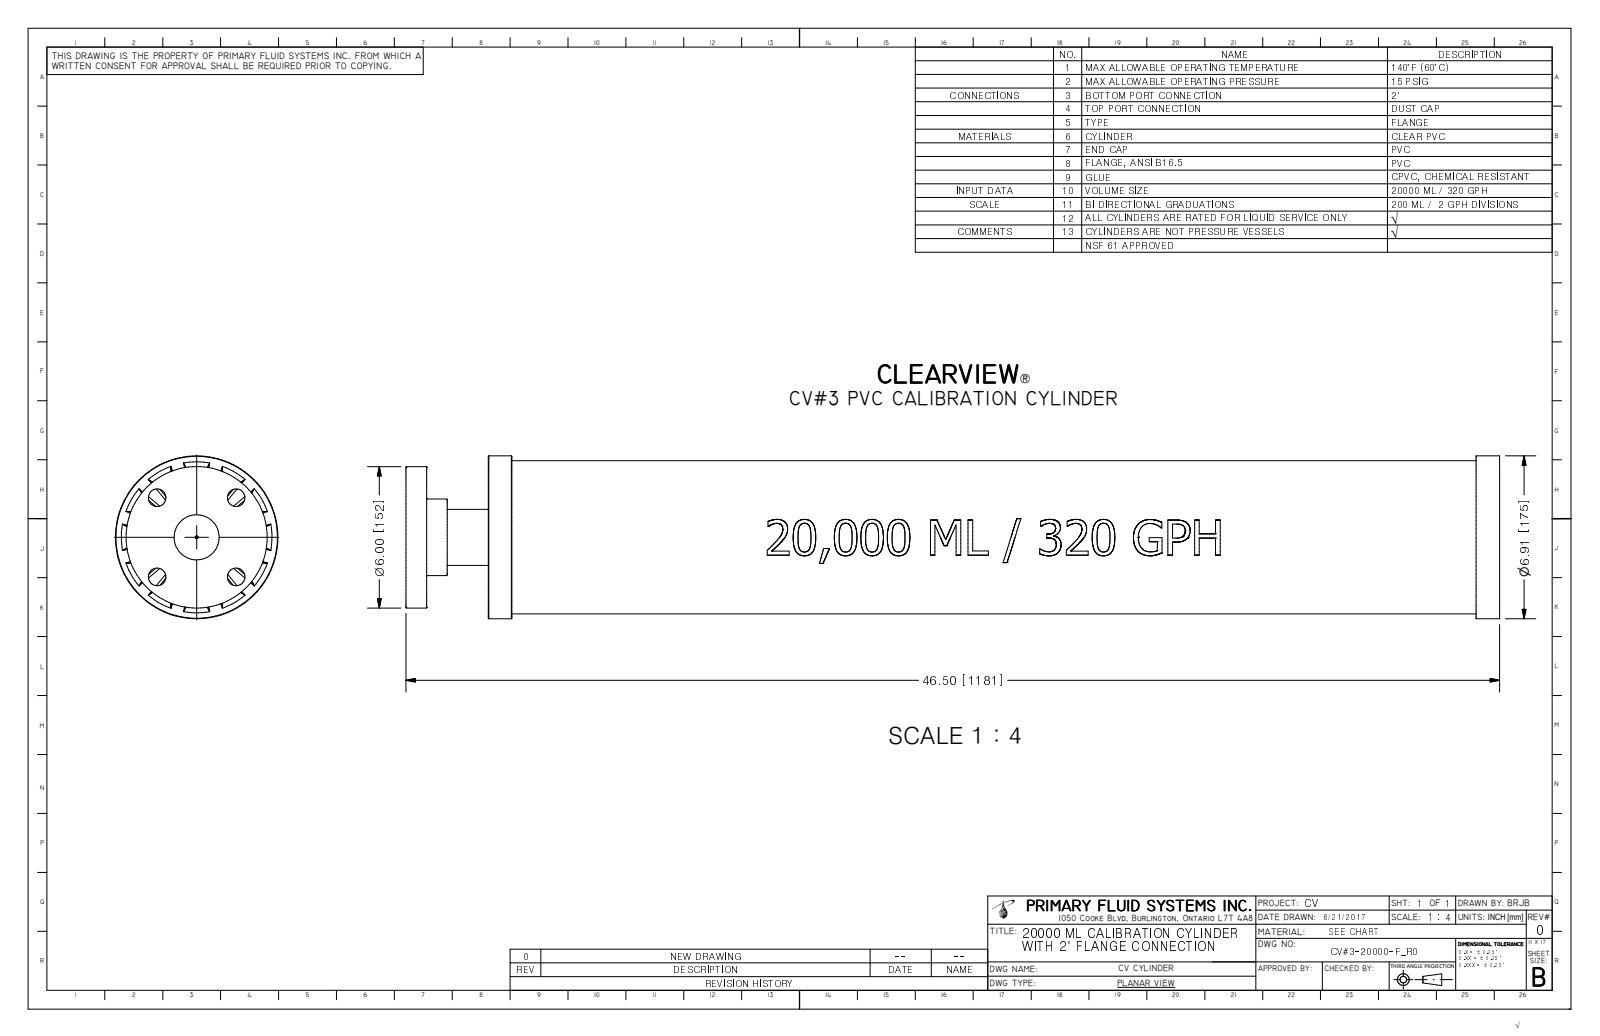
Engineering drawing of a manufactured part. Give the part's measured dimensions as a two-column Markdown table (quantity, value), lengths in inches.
| quantity | value |
| --- | --- |
| part name | PV#3-20000-F_R0 |
| STEP written by | Autodesk Inventor 2009 (AUTOMOTIVE_DESIGN) |
| units | inches |
| bodies | 1 solid, 341 faces (99 planar, 35 cylindrical, 207 other) |
| overall size | 46.5 × 6.906 × 6.906 |
| volume | 166.4 in³ |
| surface area | 2 062 in² |
| round holes (diameter × count) | 0.745 × 4, 1.913 × 1, 1.939 × 1, 6.32 × 1 |
| round bosses / shafts (diameter × count) | 6.906 × 1, 6.5 × 1, 6 × 1, 3.244 × 1, 2.375 × 1 |
| partial cylindrical surfaces (radius × count) | 3.249 × 1 |
| main face-to-face distances | 1, 45.5, 46.5, 0.885, 44.615, 45.615, 4, 3.115, 41.5, 42.5 |
| hole center spacings | 2.375, 3.359, 4.75 |
